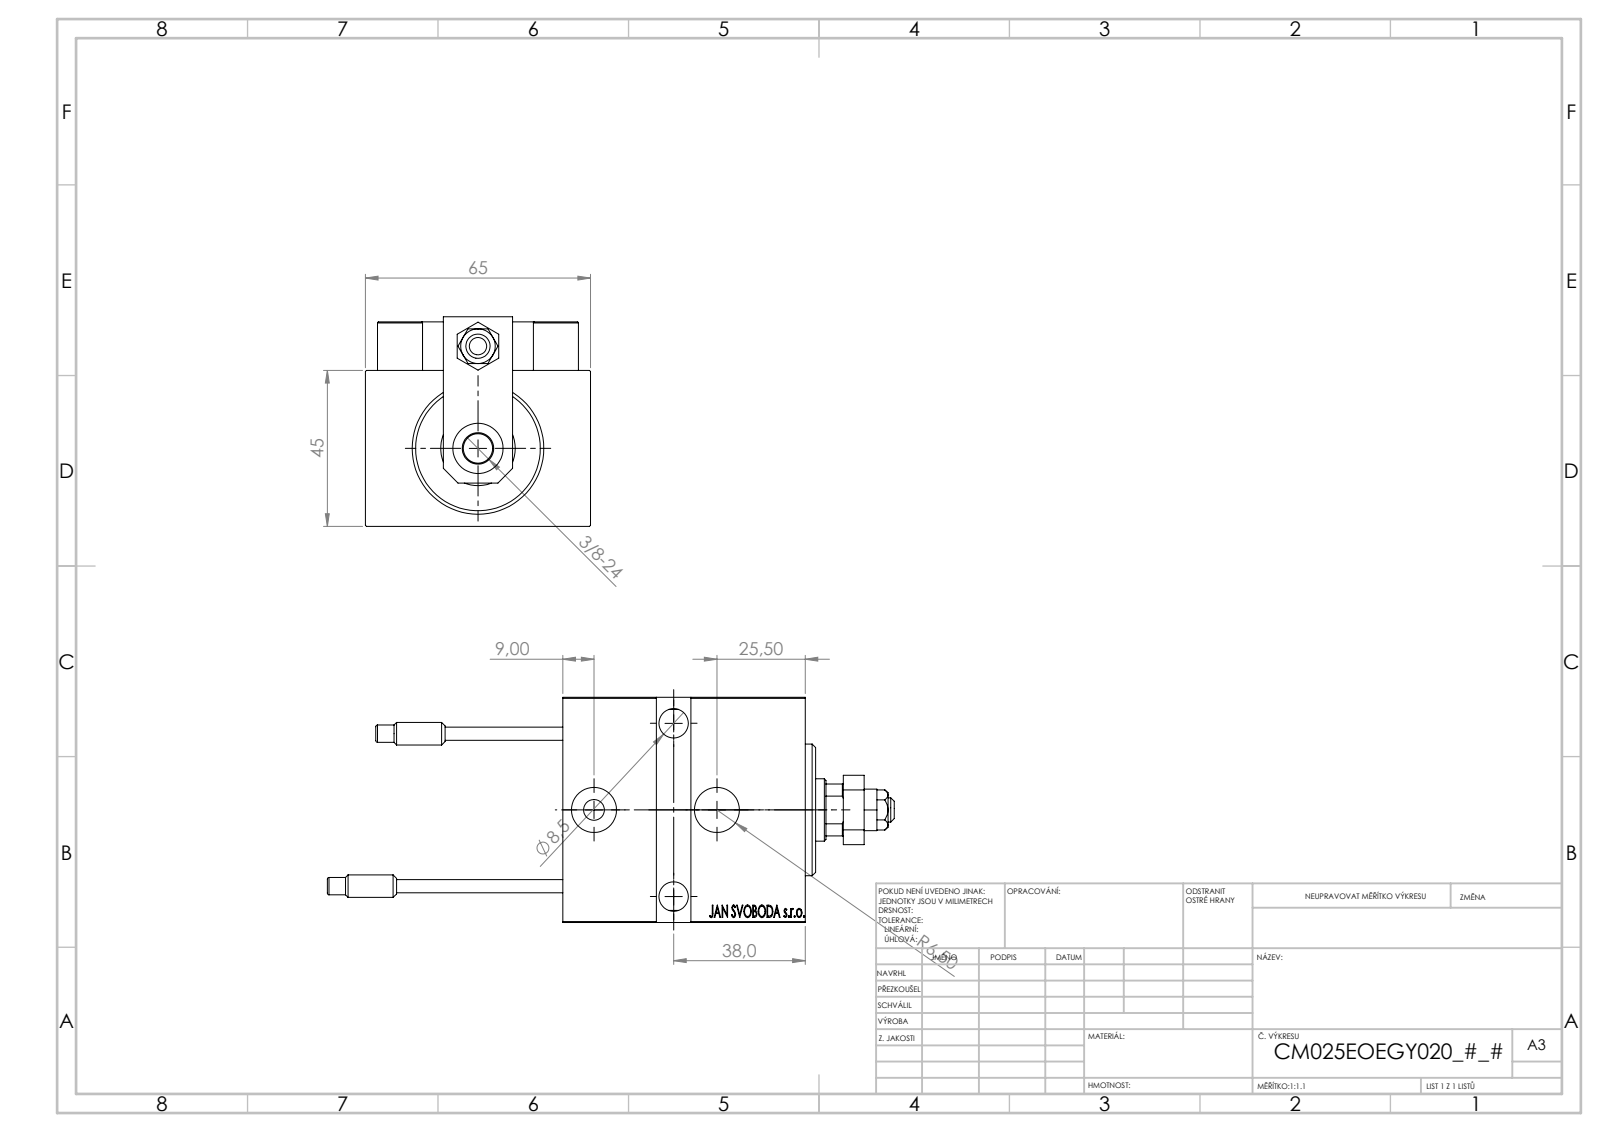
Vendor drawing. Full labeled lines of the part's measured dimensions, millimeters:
Part name (STEP PRODUCT): SWITCH_X_FRONT_BACK; SWITCH DIM B,W; V450CM_E_VCP; V450CM_VC_B (+8 more)
STEP written by: SolidWorks 2019 (CONFIG_CONTROL_DESIGN)
Units: millimetres
Bodies: 24 solids, 1298 faces (569 planar, 176 cylindrical, 553 other)
Overall size (bounding box): 163.7 × 65 × 60.5
Volume: 241 354 mm³ · Surface area: 63 149 mm²
Round holes (diameter × count): ⌀8 ×5, ⌀3.2 ×4, ⌀4 ×4, ⌀8.5 ×3, ⌀5 ×2, ⌀13 ×2, ⌀13.5 ×2, ⌀7 ×1, ⌀14.5 ×1, ⌀18 ×1, ⌀21.5 ×1, ⌀25 ×1
Round bosses / shafts (diameter × count): ⌀5 ×4, ⌀6.5 ×2, ⌀3.8 ×2, ⌀38 ×1, ⌀27 ×1, ⌀13 ×1, ⌀11 ×1, ⌀6 ×1
Partial cylindrical surfaces — rounded edges, fillets, slot ends (radius × count): R0.3 ×30, R3 ×2, R8.5 ×1
Main face-to-face distances: 45, 65, 14, 59, 6, 19, 8, 70, 58, 13
Hole centre spacings: 10.77, 11.37, 20, 21.03, 22.09, 27.95, 29.59, 29.69
